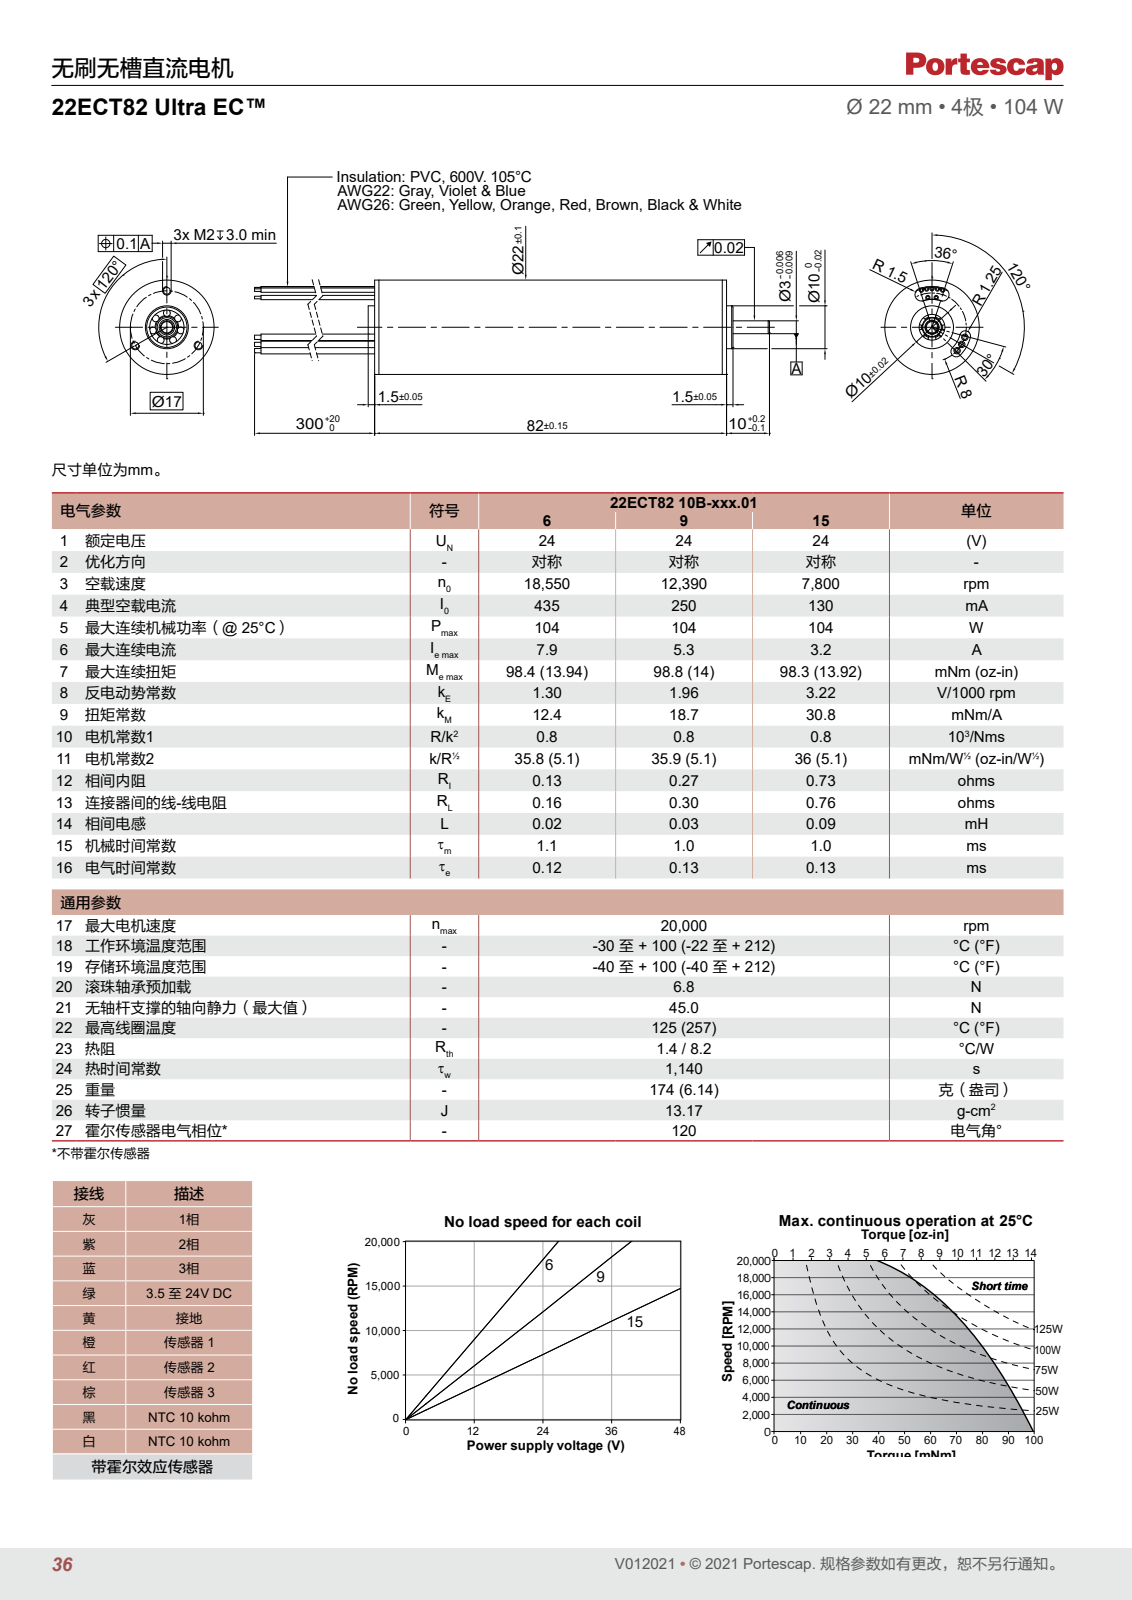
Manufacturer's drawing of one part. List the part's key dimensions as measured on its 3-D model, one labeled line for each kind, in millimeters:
Part name (STEP PRODUCT): 22ECT82_ASM
STEP written by: PRO/ENGINEER BY PARAMETRIC TECHNOLOGY CORPORATION, 2014310 (CONFIG_CONTROL_DESIGN)
Units: millimetres
Bodies: 11 solids, 250 faces (47 planar, 111 cylindrical, 92 other)
Overall size (bounding box): 167.55 × 22.15 × 22
Volume: 31 784 mm³ · Surface area: 9 435 mm²
Round holes (diameter × count): ⌀1.6 ×3, ⌀6 ×1, ⌀6.4 ×1, ⌀8 ×1, ⌀8.2 ×1
Round bosses / shafts (diameter × count): ⌀1 ×10, ⌀0.6 ×7, ⌀1.5 ×3, ⌀22 ×1, ⌀21 ×1, ⌀10 ×1, ⌀5.08 ×1, ⌀4.6 ×1
Partial cylindrical surfaces — rounded edges, fillets, slot ends (radius × count): R1 ×4, R1.25 ×2, R1.5 ×2, R6.5 ×1, R6.75 ×1, R9.25 ×1, R9.5 ×1, R11.15 ×1
Main face-to-face distances: 82, 1.5, 83.5, 1, 82.5, 3.56, 2.06, 79.94, 80.2, 78.7
Hole centre spacings: 8.5, 14.72
